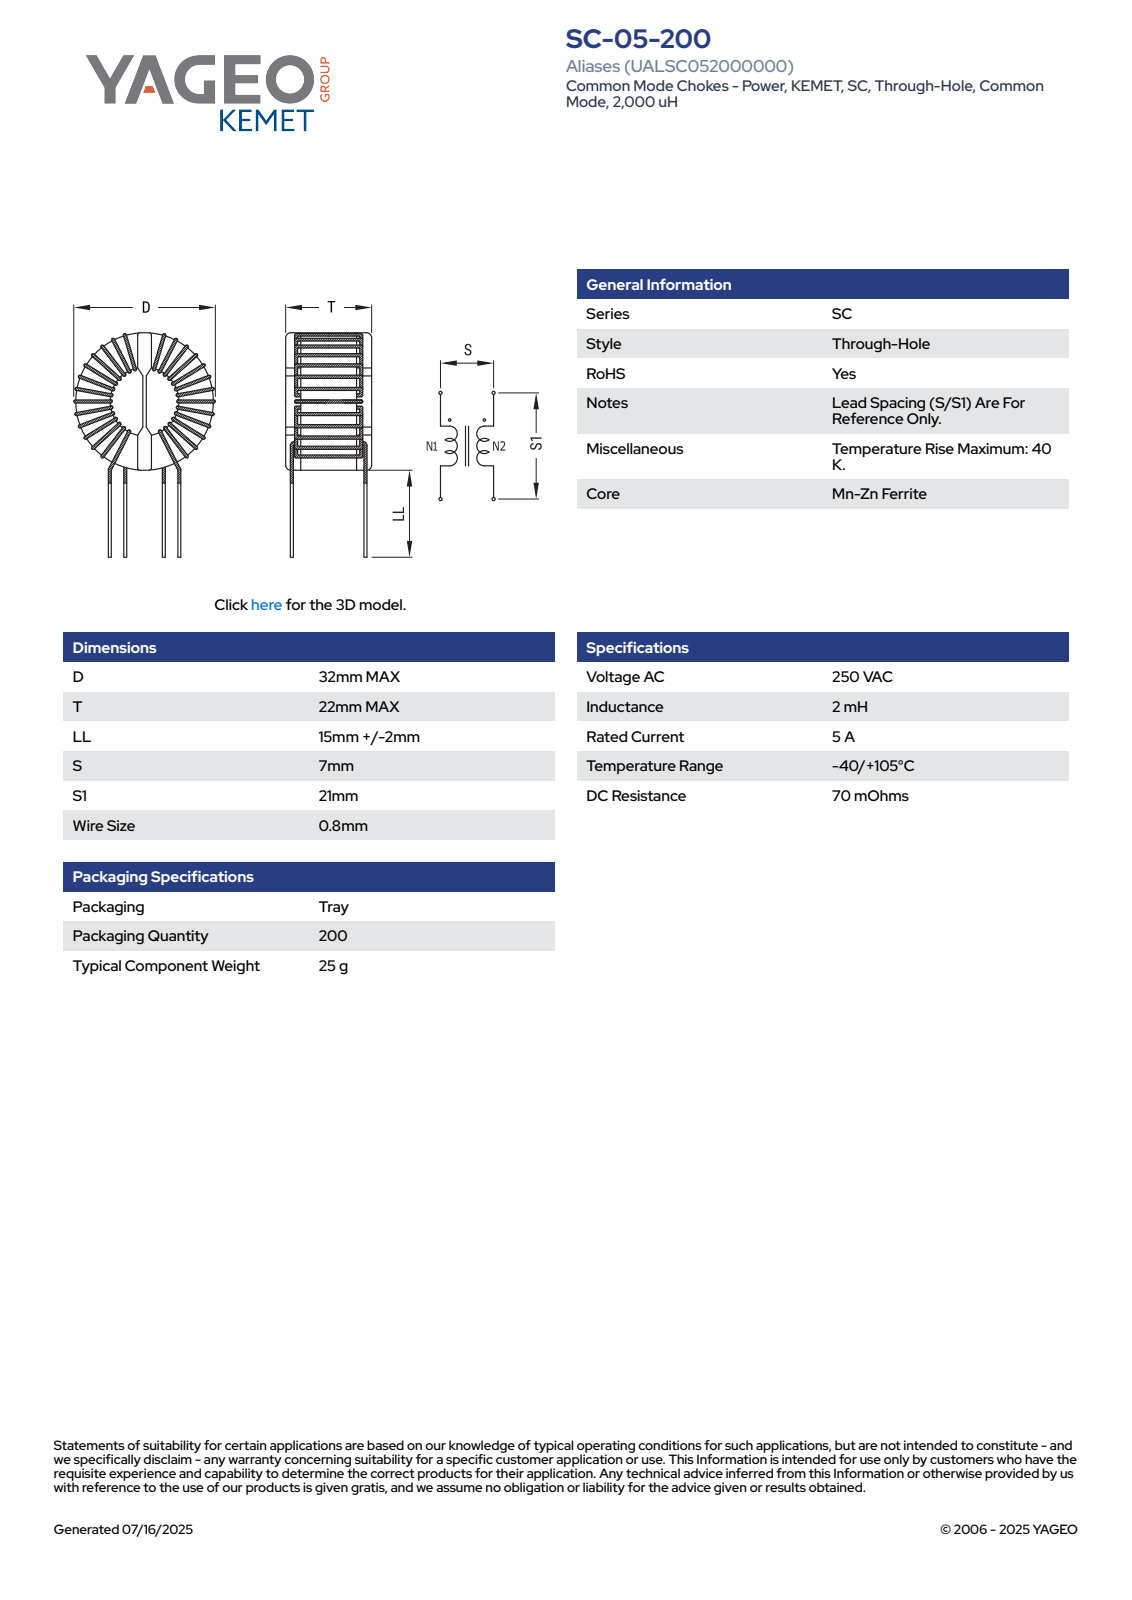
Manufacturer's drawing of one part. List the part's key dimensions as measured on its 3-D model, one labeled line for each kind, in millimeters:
Part name (STEP PRODUCT): SC-05-200
STEP written by: SolidWorks 2018 (AUTOMOTIVE_DESIGN)
Units: millimetres
Bodies: 1 solid, 273 faces (113 planar, 91 cylindrical, 69 other)
Overall size (bounding box): 44.3 × 32 × 22
Volume: 13 625 mm³ · Surface area: 6 031 mm²
Round bosses / shafts (diameter × count): ⌀0.8 ×8
Partial cylindrical surfaces — rounded edges, fillets, slot ends (radius × count): R0.4 ×16, R0.2 ×6, R0.5 ×2, R4.5 ×1, R6.65 ×1, R7.35 ×1, R7.45 ×1, R7.5 ×1
Main face-to-face distances: 20.2, 1.2, 2, 0.8, 3.2, 0.9, 21.1, 2.5, 18.6, 17.7
